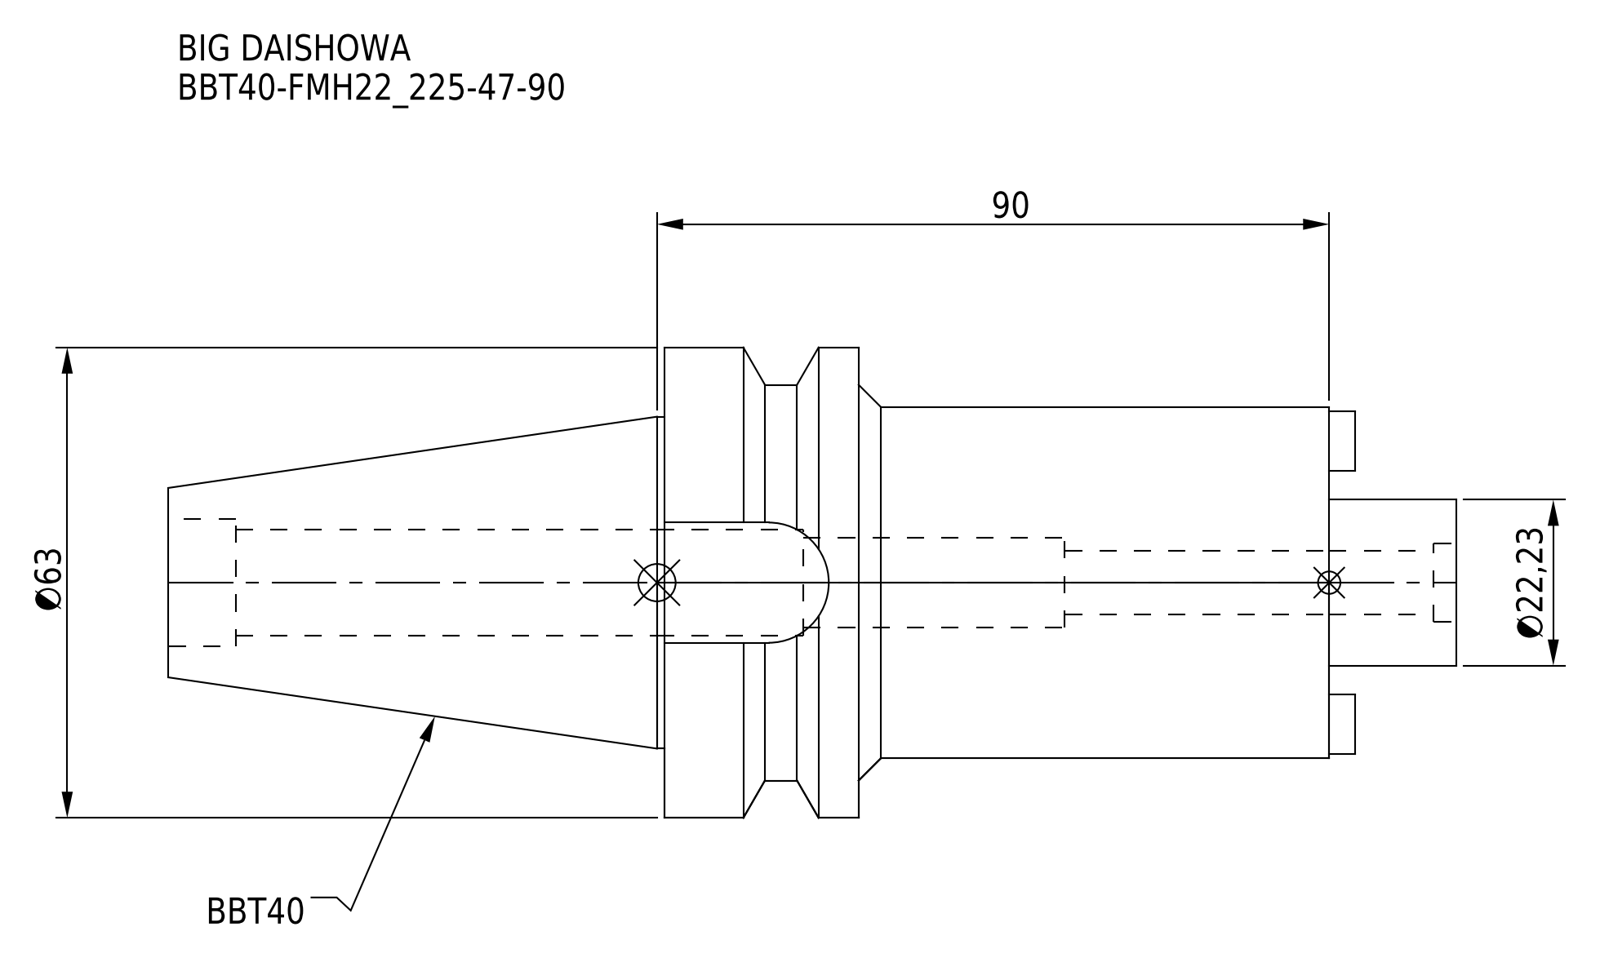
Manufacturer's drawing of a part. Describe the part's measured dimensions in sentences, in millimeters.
The part is named "BBT40-FMH22_225-47-90". Its 3-D file was written by "CREO PARAMETRIC BY PTC INC, 2016380 (AUTOMOTIVE_DESIGN)". It is 1 solid with 61 faces: 25 planar, 28 cylindrical and 8 other. Overall it measures 172.4 by 63 by 63 millimeters. Its volume is 231 517 cubic millimeters and its surface area 35 773 square millimeters. Round holes: 1 of diameter 8.5, 1 of diameter 10.5, 1 of diameter 12, 1 of diameter 14.2, 1 of diameter 17. Round bosses or shafts: 1 of diameter 63, 1 of diameter 53, 1 of diameter 47, 1 of diameter 44.45, 1 of diameter 22.23. Partial cylindrical surfaces (rounded edges, fillets, slot ends): 1 of radius 8.05. The main face-to-face distances are 89, 63, 26, 45, 17, 80, 106, 172.4, 155.4, 92.4.
